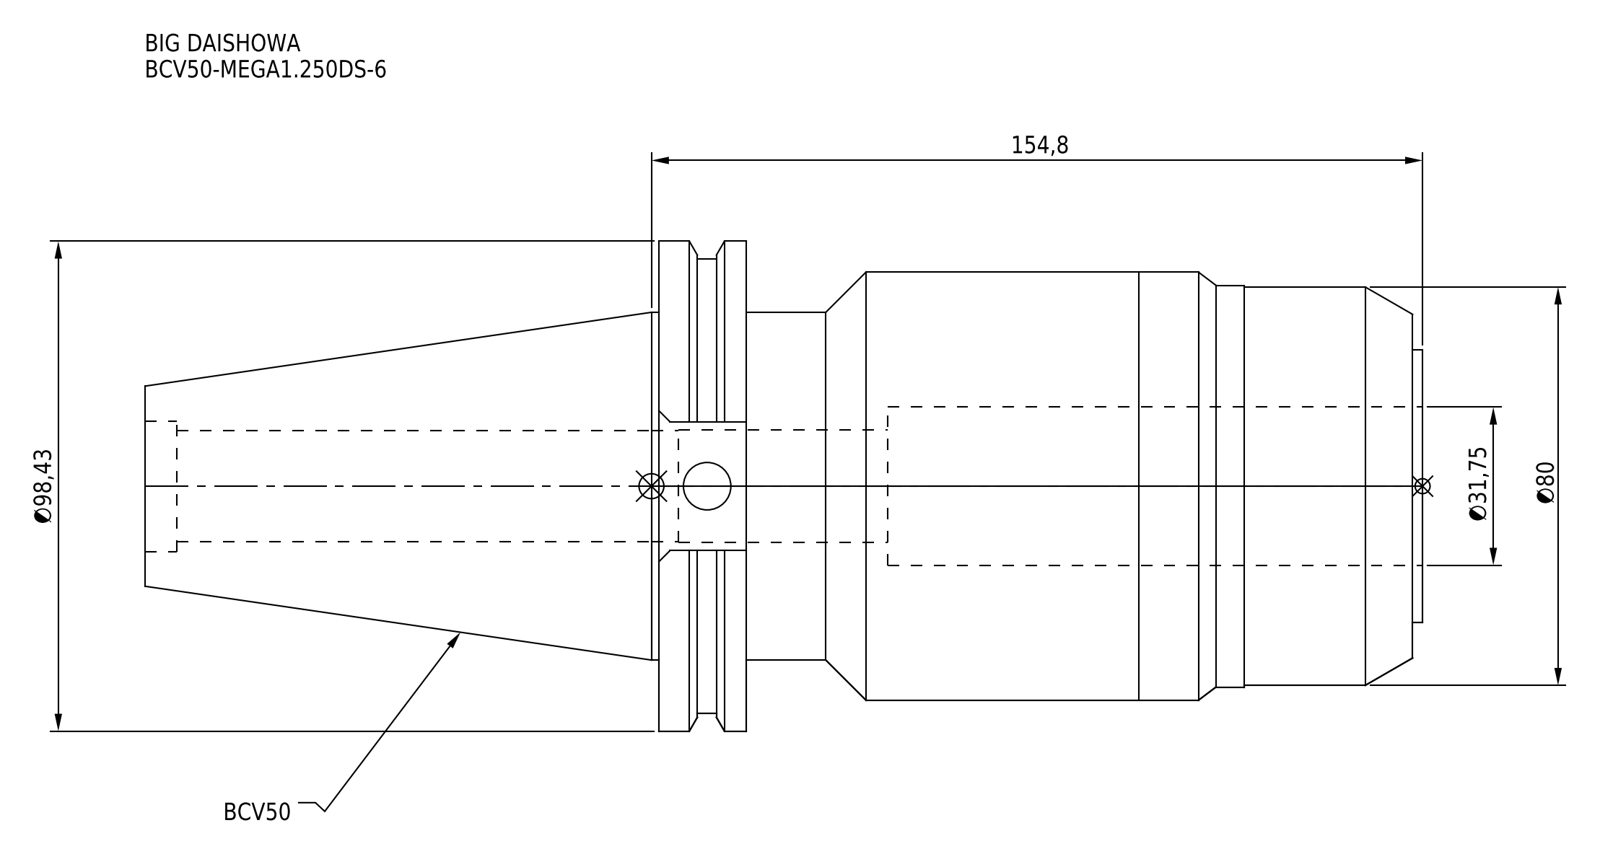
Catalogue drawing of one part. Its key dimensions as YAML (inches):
part_name: "BCV50-MEGA1_250DS-6"
step_written_by: "CREO PARAMETRIC BY PTC INC, 2016380 (AUTOMOTIVE_DESIGN)"
units: inches
bodies: {solids: 1, faces: 66, planar: 24, cylindrical: 30, other: 12}
overall_size: [10.094, 3.875, 3.738]
volume: 56.79
surface_area: 144.2
round_holes:
  - {diameter: 0.375, count: 1}
  - {diameter: 0.878, count: 1}
  - {diameter: 0.886, count: 1}
  - {diameter: 1.033, count: 1}
  - {diameter: 1.25, count: 1}
round_bosses_or_shafts:
  - {diameter: 3.875, count: 1}
  - {diameter: 3.594, count: 1}
  - {diameter: 3.386, count: 1}
  - {diameter: 3.177, count: 1}
  - {diameter: 3.15, count: 1}
  - {diameter: 2.75, count: 1}
  - {diameter: 2.154, count: 1}
face_to_face_distances: [0.691, 5.344, 6.035, 0.079, 5.266, 5.957, 10.094, 10.016, 4.75, 4.059]
